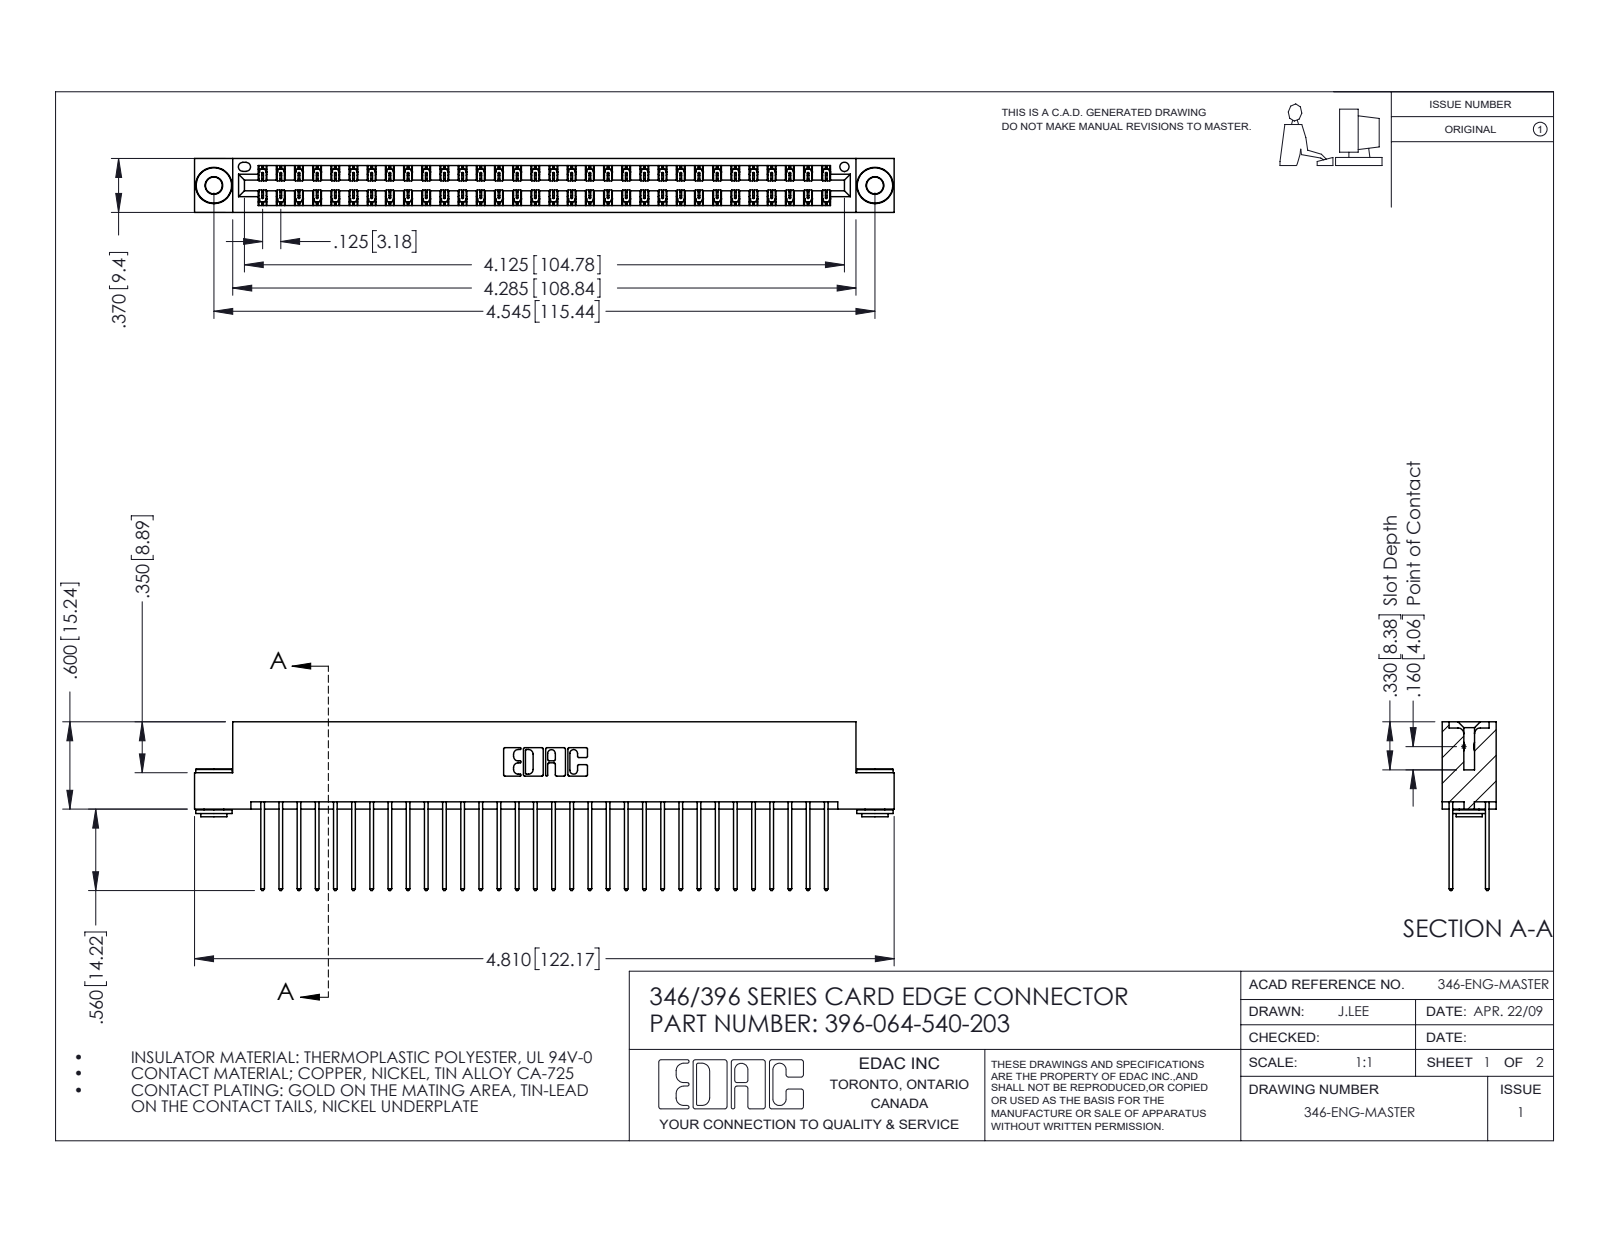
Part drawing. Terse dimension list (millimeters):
name: 345-292-001_345-293-140; 396-064-540-203; 346 Part_Flush Mounting Lugs - 0.156 Dia-TH; 345-250-002_345-250-002-102
written by: SolidWorks 2016 (CONFIG_CONTROL_DESIGN)
unit: mm
bodies: 67 solids, 3488 faces (2326 planar, 1154 cylindrical, 8 other)
size: 122.2 × 29.5 × 9.4
volume: 12 100 mm³; area: 17 830 mm²
holes: 2× ⌀2.9, 2× ⌀4, 1× ⌀1.6
bosses: 2× ⌀6.4, 2× ⌀4.6, 2× ⌀3.5
rounds: 96× R0.2, 64× R0.3, 22× R0.3, 6× R0.2, 6× R0.8, 3× R0.7, 2× R0.4, 2× R0.6
face distances: 1.2, 8.2, 6.4, 0.6, 1.8, 7.6, 9.4, 7, 3.8, 5.6
hole spacings: 6.2, 110.2, 115.4
